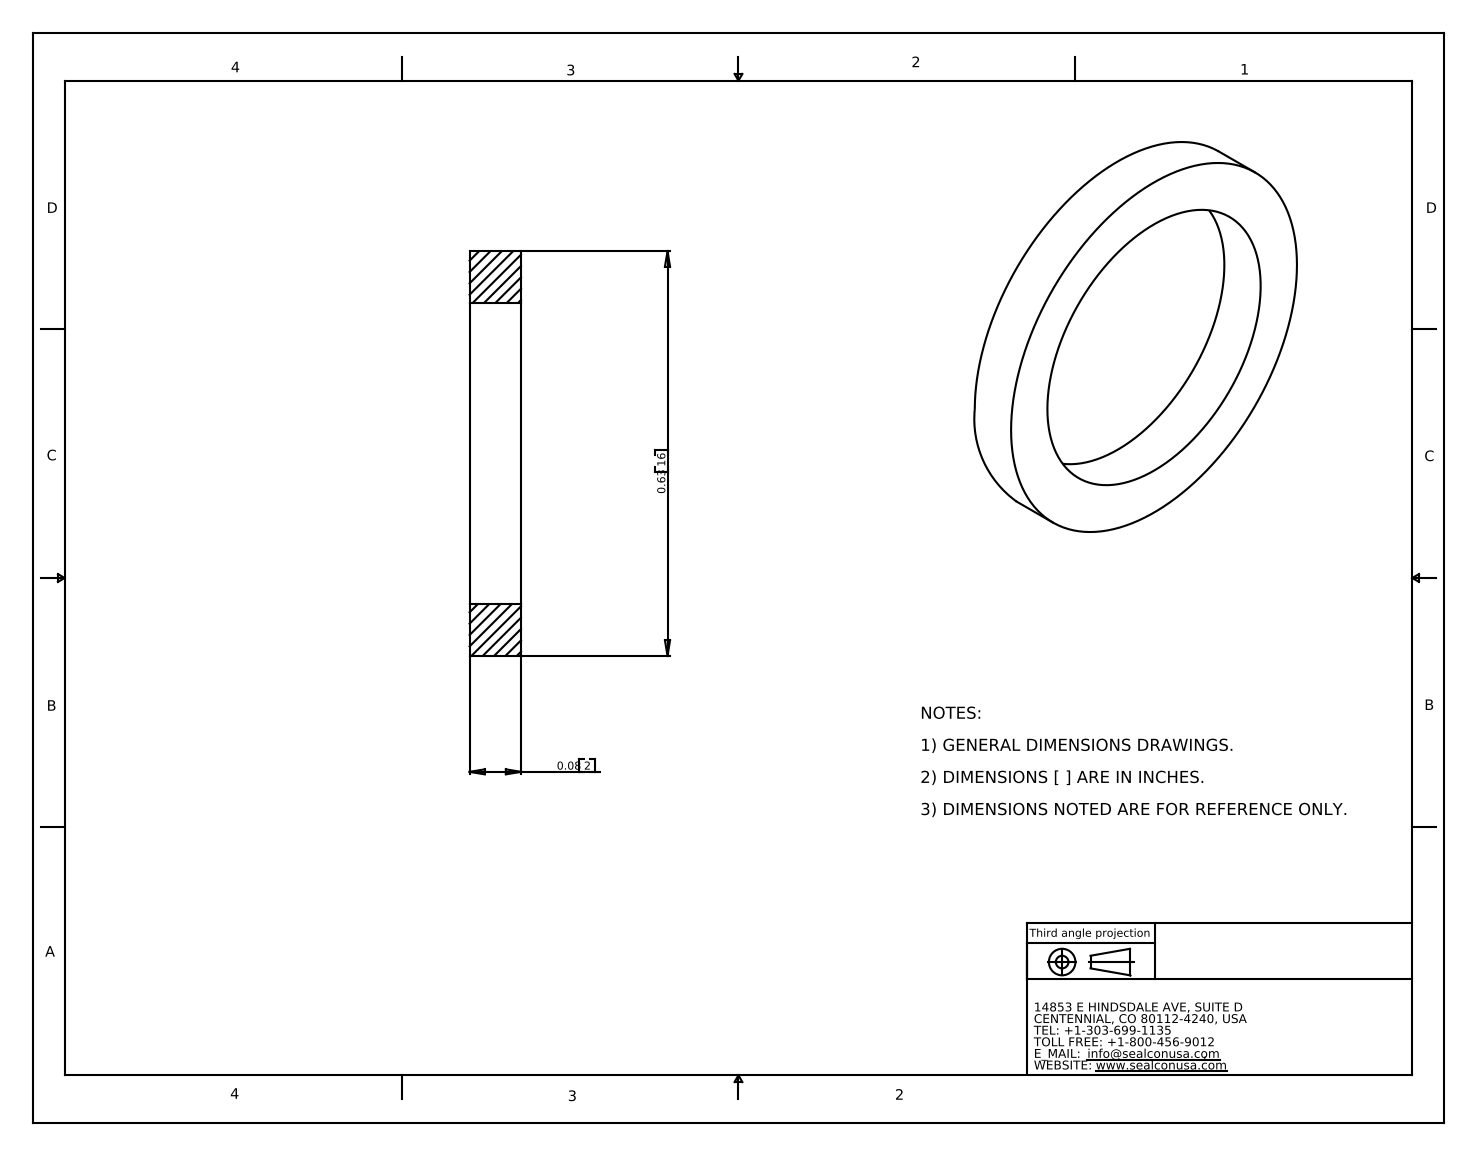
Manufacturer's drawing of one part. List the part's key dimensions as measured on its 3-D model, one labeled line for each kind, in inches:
Part name (STEP PRODUCT): SM-12-VT
STEP written by: SolidWorks 2007 (CONFIG_CONTROL_DESIGN)
Units: inches
Bodies: 1 solid, 6 faces (2 planar, 4 cylindrical, 0 other)
Overall size (bounding box): 0.63 × 0.63 × 0.08
Volume: 0.011 in³ · Surface area: 0.553 in²
Round holes (diameter × count): ⌀0.47 ×1
Round bosses / shafts (diameter × count): ⌀0.63 ×1
Main face-to-face distances: 0.08
